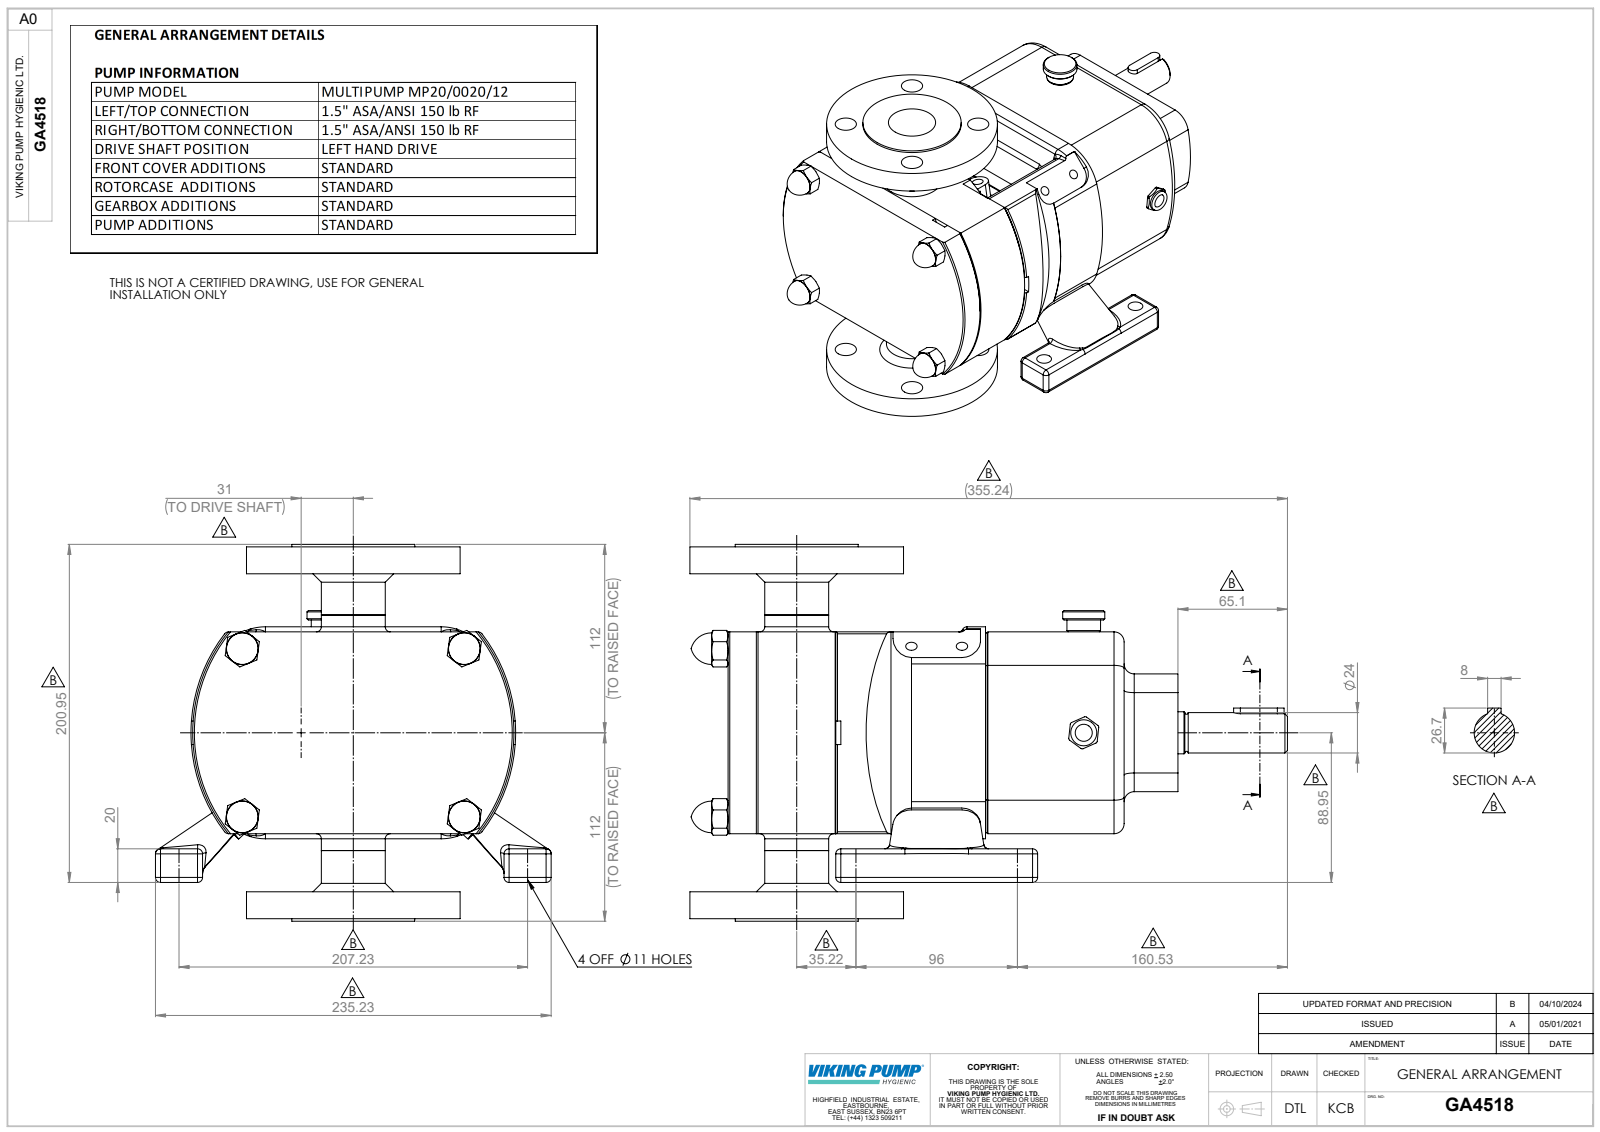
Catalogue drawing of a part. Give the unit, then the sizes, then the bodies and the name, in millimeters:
Units: millimetres
Overall size (bounding box): 355.24 × 235.23 × 224
Round holes (diameter × count): ⌀15.8 ×6, ⌀6.8 ×4, ⌀11 ×4, ⌀8 ×2, ⌀22.53 ×1, ⌀35.1 ×1
Round bosses / shafts (diameter × count): ⌀35 ×2, ⌀127 ×1, ⌀73.1 ×1, ⌀38 ×1, ⌀25.02 ×1, ⌀25 ×1, ⌀24 ×1, ⌀19.99 ×1
Partial cylindrical surfaces — rounded edges, fillets, slot ends (radius × count): R3 ×60, R2 ×18, R1 ×16, R6 ×8, R11.1 ×8, R1.27 ×6, R4 ×6, R8 ×6
Main face-to-face distances: 34.5, 154.5, 120, 16, 50.5, 170.5, 205, 189, 109.04, 158.4
Hole centre spacings: 49.2, 69.58, 30.05, 49.19, 68.83, 69.54, 69.61, 96
Volume: 5 114 000 mm³ · Surface area: 357 826 mm²
Bodies: 3 solids, 805 faces (241 planar, 297 cylindrical, 267 other)
Part name (STEP PRODUCT): GA4518; Copy of Z94-5301-22 - 1.5 INCH ASA 150^GA4518; Copy of CP20-0020-12 V L^GA4518
STEP written by: SolidWorks 2023 (AUTOMOTIVE_DESIGN)
